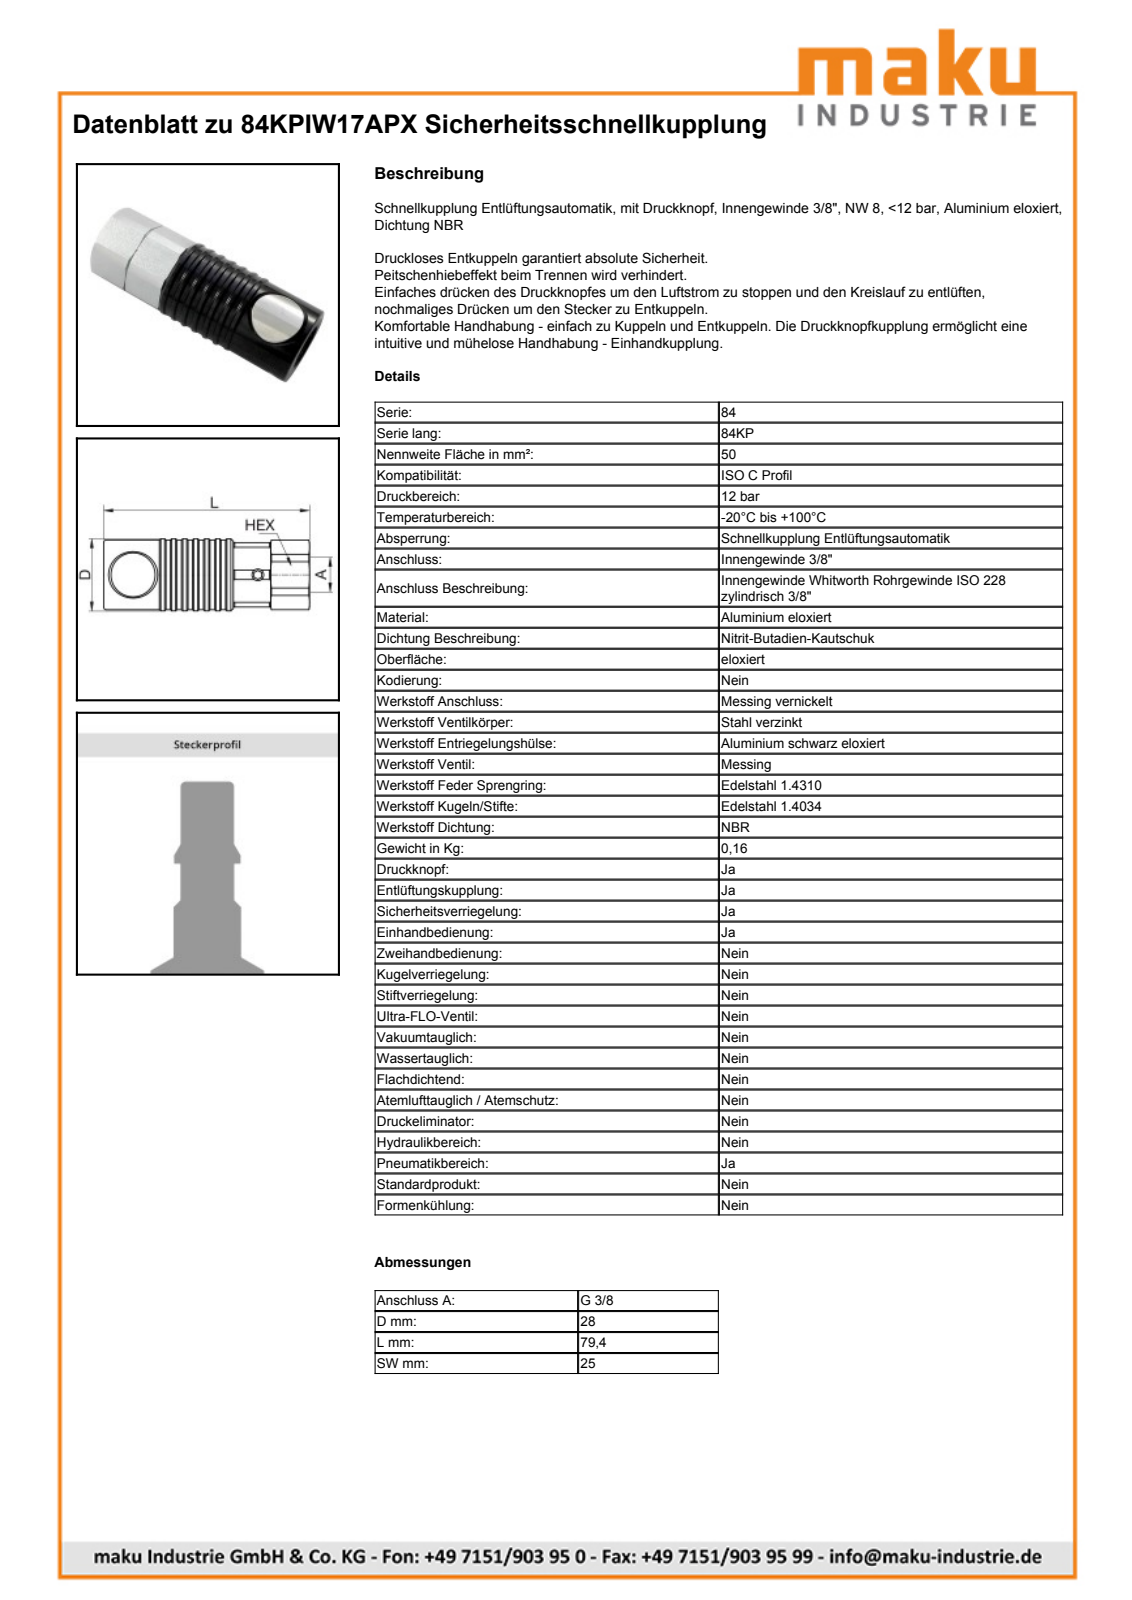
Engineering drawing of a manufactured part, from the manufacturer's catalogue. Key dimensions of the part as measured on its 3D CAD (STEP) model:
Part name (STEP PRODUCT): 84KPIW17APX
STEP written by: Autodesk Inventor 2019 (CONFIG_CONTROL_DESIGN)
Units: millimetres
Bodies: 33 solids, 345 faces (114 planar, 123 cylindrical, 108 other)
Overall size (bounding box): 79.4 × 28 × 28
Volume: 53 665 mm³ · Surface area: 31 177 mm²
Round holes (diameter × count): ⌀3.5 ×2, ⌀4 ×2, ⌀14 ×2, ⌀7.9 ×1, ⌀8 ×1, ⌀11.2 ×1, ⌀14.1 ×1, ⌀15 ×1, ⌀15.5 ×1, ⌀16.7 ×1, ⌀16.75 ×1, ⌀17.1 ×1
Round bosses / shafts (diameter × count): ⌀28 ×1, ⌀27 ×1, ⌀25 ×1, ⌀23.33 ×1, ⌀23.3 ×1, ⌀23 ×1, ⌀22.24 ×1, ⌀19.7 ×1
Partial cylindrical surfaces — rounded edges, fillets, slot ends (radius × count): R5.53 ×1, R8.5 ×1, R9.3 ×1, R9.75 ×1, R13.5 ×1, R14.5 ×1
Main face-to-face distances: 25, 64.4, 35.3, 29.1, 24.3, 0.98, 36.28, 65.38, 6.4, 10
Hole centre spacings: 1.2, 1.3, 22, 26.1, 48.1
